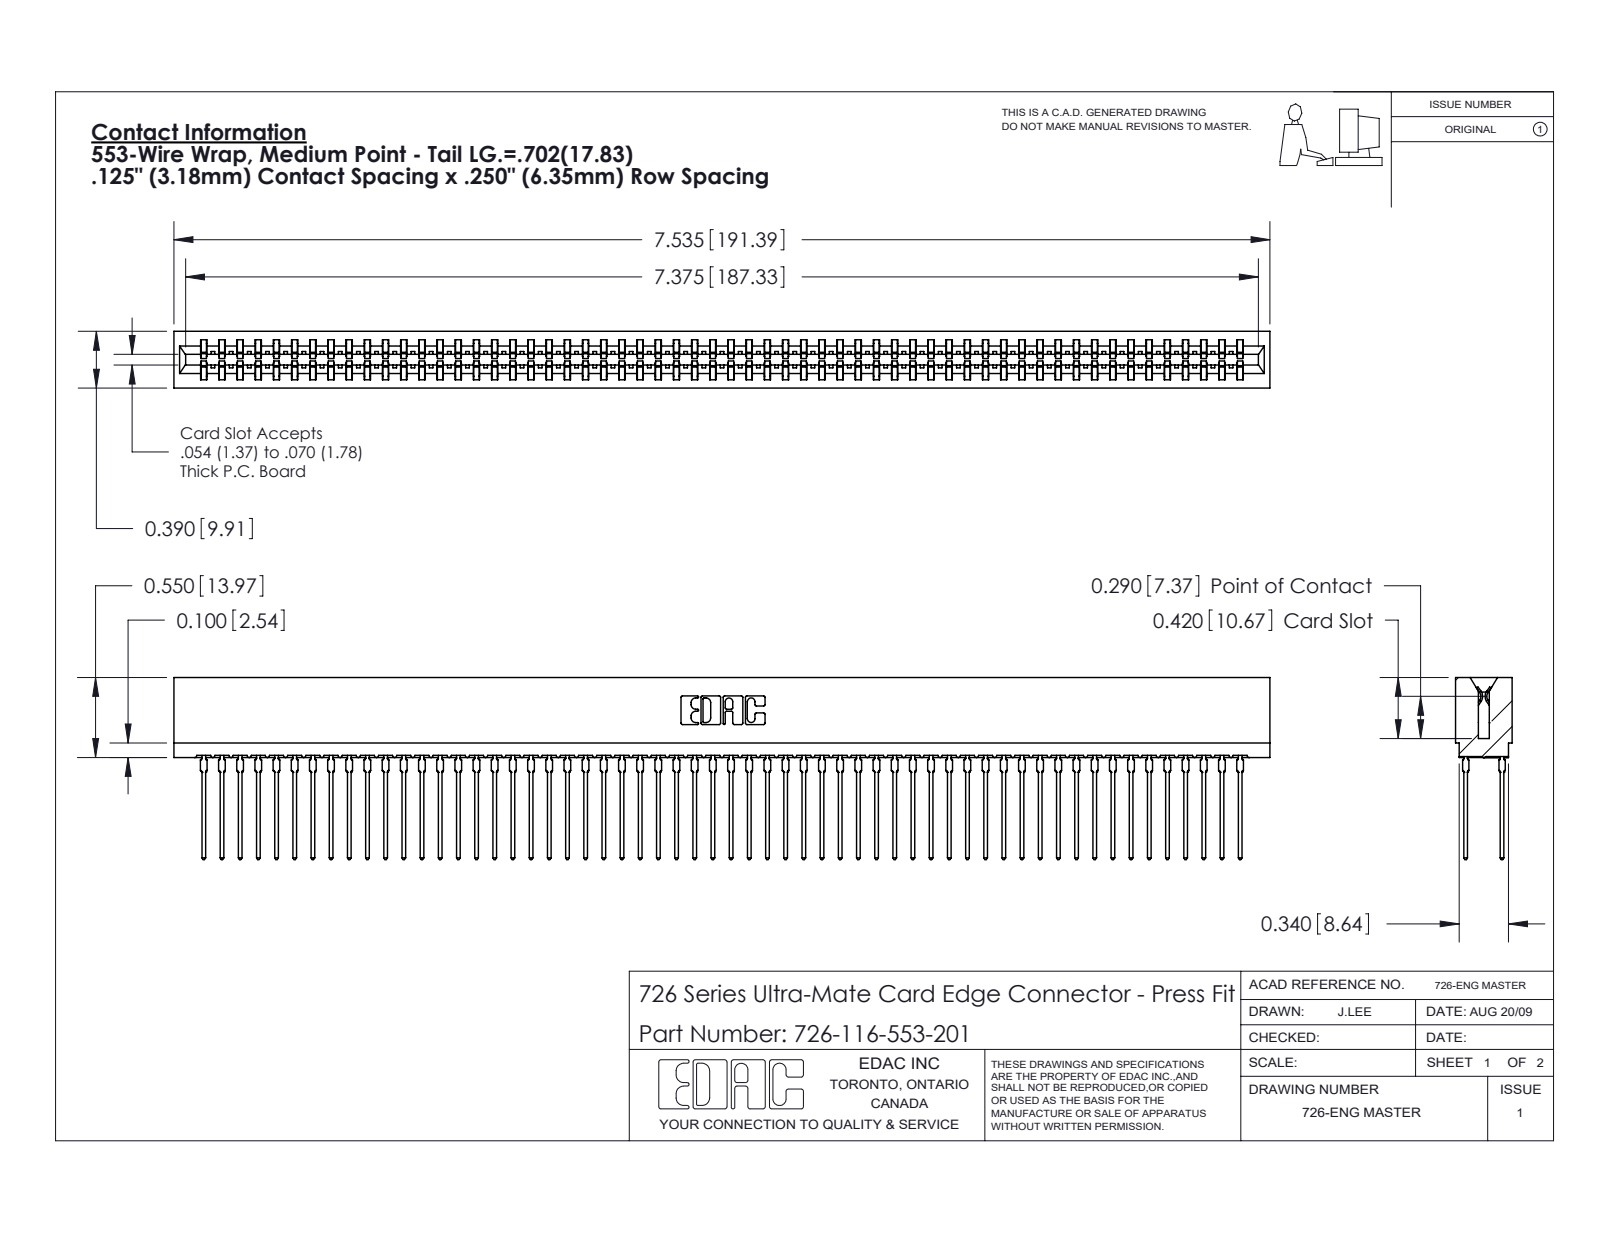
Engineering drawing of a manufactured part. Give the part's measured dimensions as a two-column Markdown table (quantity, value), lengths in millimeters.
| quantity | value |
| --- | --- |
| part name | 726 Part_.515 Slot Depth - 01; 726-116-553-201; 746-292-001_553 |
| STEP written by | SolidWorks 2020 (CONFIG_CONTROL_DESIGN) |
| units | millimeters |
| bodies | 117 solids, 10479 faces (5391 planar, 2072 cylindrical, 3016 other) |
| overall size | 191.4 × 31.8 × 9.9 |
| volume | 18 060 mm³ |
| surface area | 32 710 mm² |
| partial cylindrical surfaces (radius × count) | 0.5 × 232, 0.4 × 59, 0.3 × 22, 0.1 × 8, 0.3 × 8, 0.2 × 6, 0.8 × 6, 0.7 × 3 |
| main face-to-face distances | 1.4, 8.5, 0.6, 7.8, 9.9, 6.4, 2.1, 7, 5.7, 9.3 |
